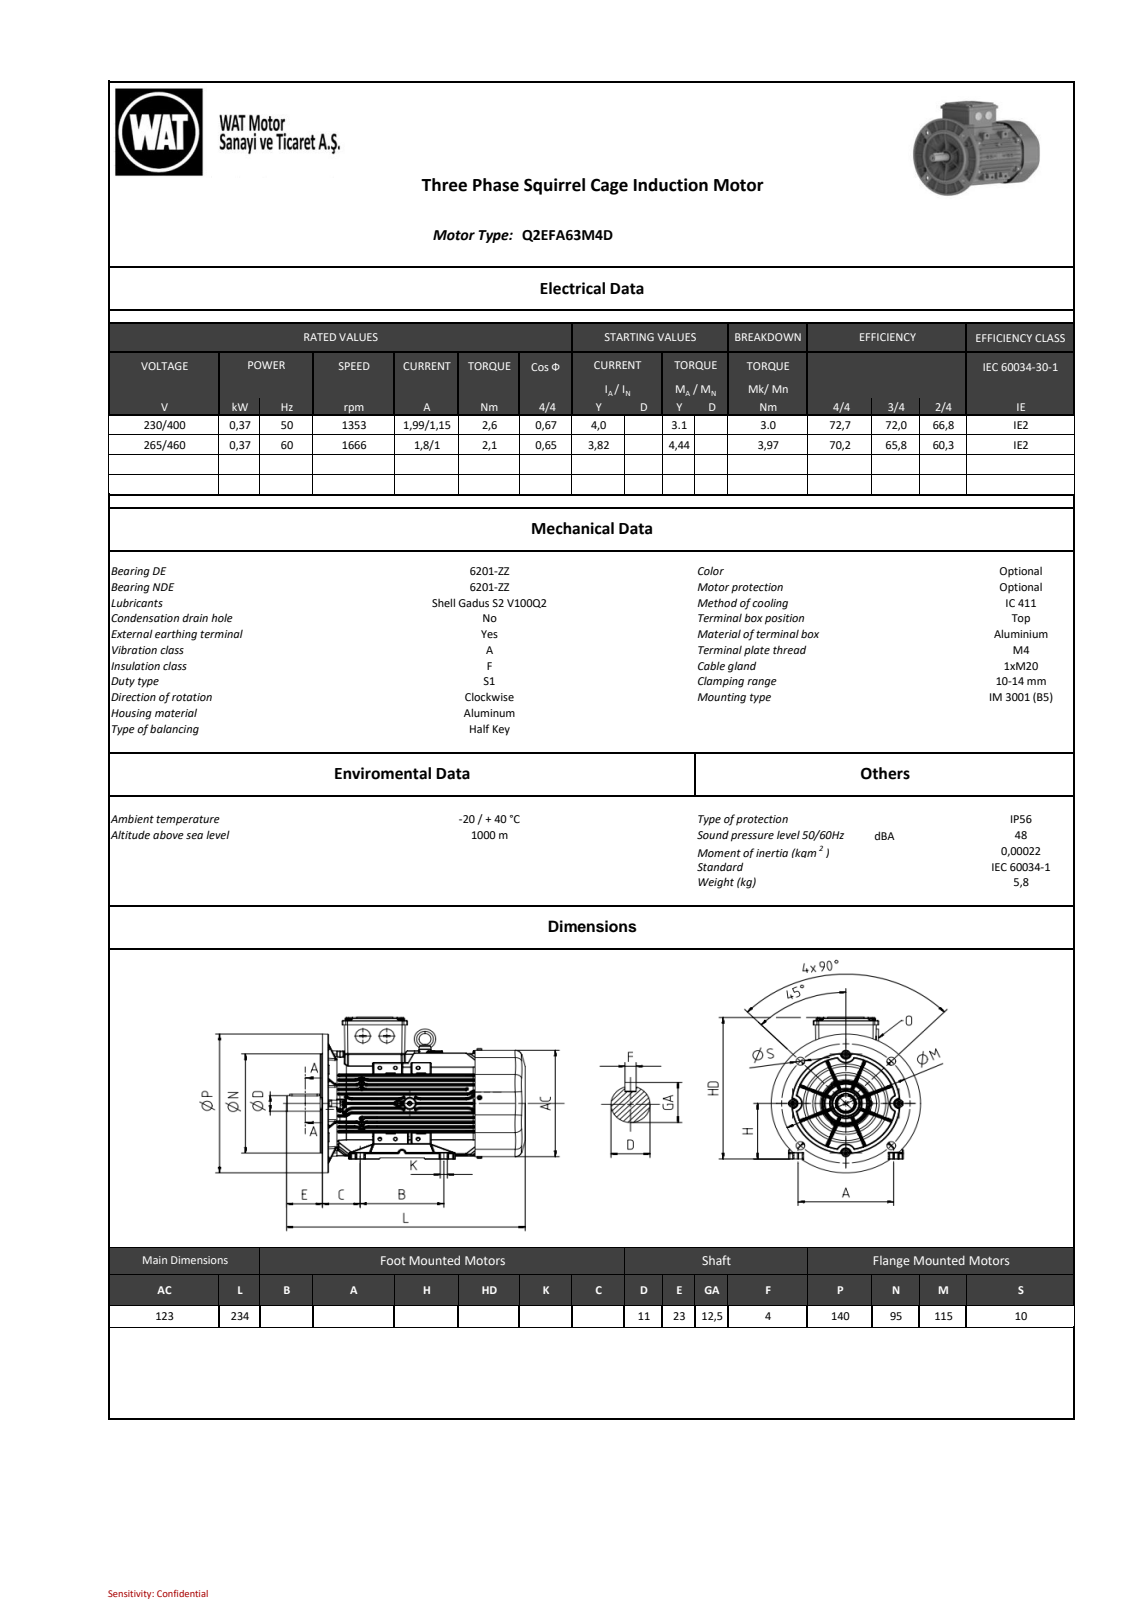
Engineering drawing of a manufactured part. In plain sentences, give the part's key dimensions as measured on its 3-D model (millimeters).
The part is named "QE Series_ 63_B5_Deep Cover__stp_objects". Its 3-D file was written by "SIEMENS PLM Software NX2206.8101 (AP203_CONFIGURATION_CONTROLLED_3D_DESIGN_OF_MECHANICAL_PARTS_AND_ASSEMBLIES_MIM_LF)". It is 0 solids with 1333 faces: 792 planar, 383 cylindrical and 158 other. Overall it measures 233.47 by 169.2 by 140.2 millimeters. Round holes: 8 of diameter 3.65, 8 of diameter 10, 4 of diameter 2.5, 2 of diameter 3, 1 of diameter 5, 1 of diameter 8, 1 of diameter 14.96, 1 of diameter 19, 1 of diameter 19.84, 1 of diameter 57, 1 of diameter 121. Round bosses or shafts: 8 of diameter 8, 4 of diameter 4.8, 3 of diameter 4, 1 of diameter 140.2, 1 of diameter 123, 1 of diameter 95, 1 of diameter 61, 1 of diameter 25.28. Partial cylindrical surfaces (rounded edges, fillets, slot ends): 106 of radius 0.5, 58 of radius 1, 16 of radius 1.5, 10 of radius 2, 8 of radius 4, 7 of radius 5, 7 of radius 8, 6 of radius 0.3. The main face-to-face distances are 7.02, 27.96, 28.05, 6.93, 13.81, 6.88, 6.02, 21.03, 1, 14.16. The hole center spacings are 44.01, 57.5, 81.32, 54, 63, 82.98, 106.24, 106.25.
